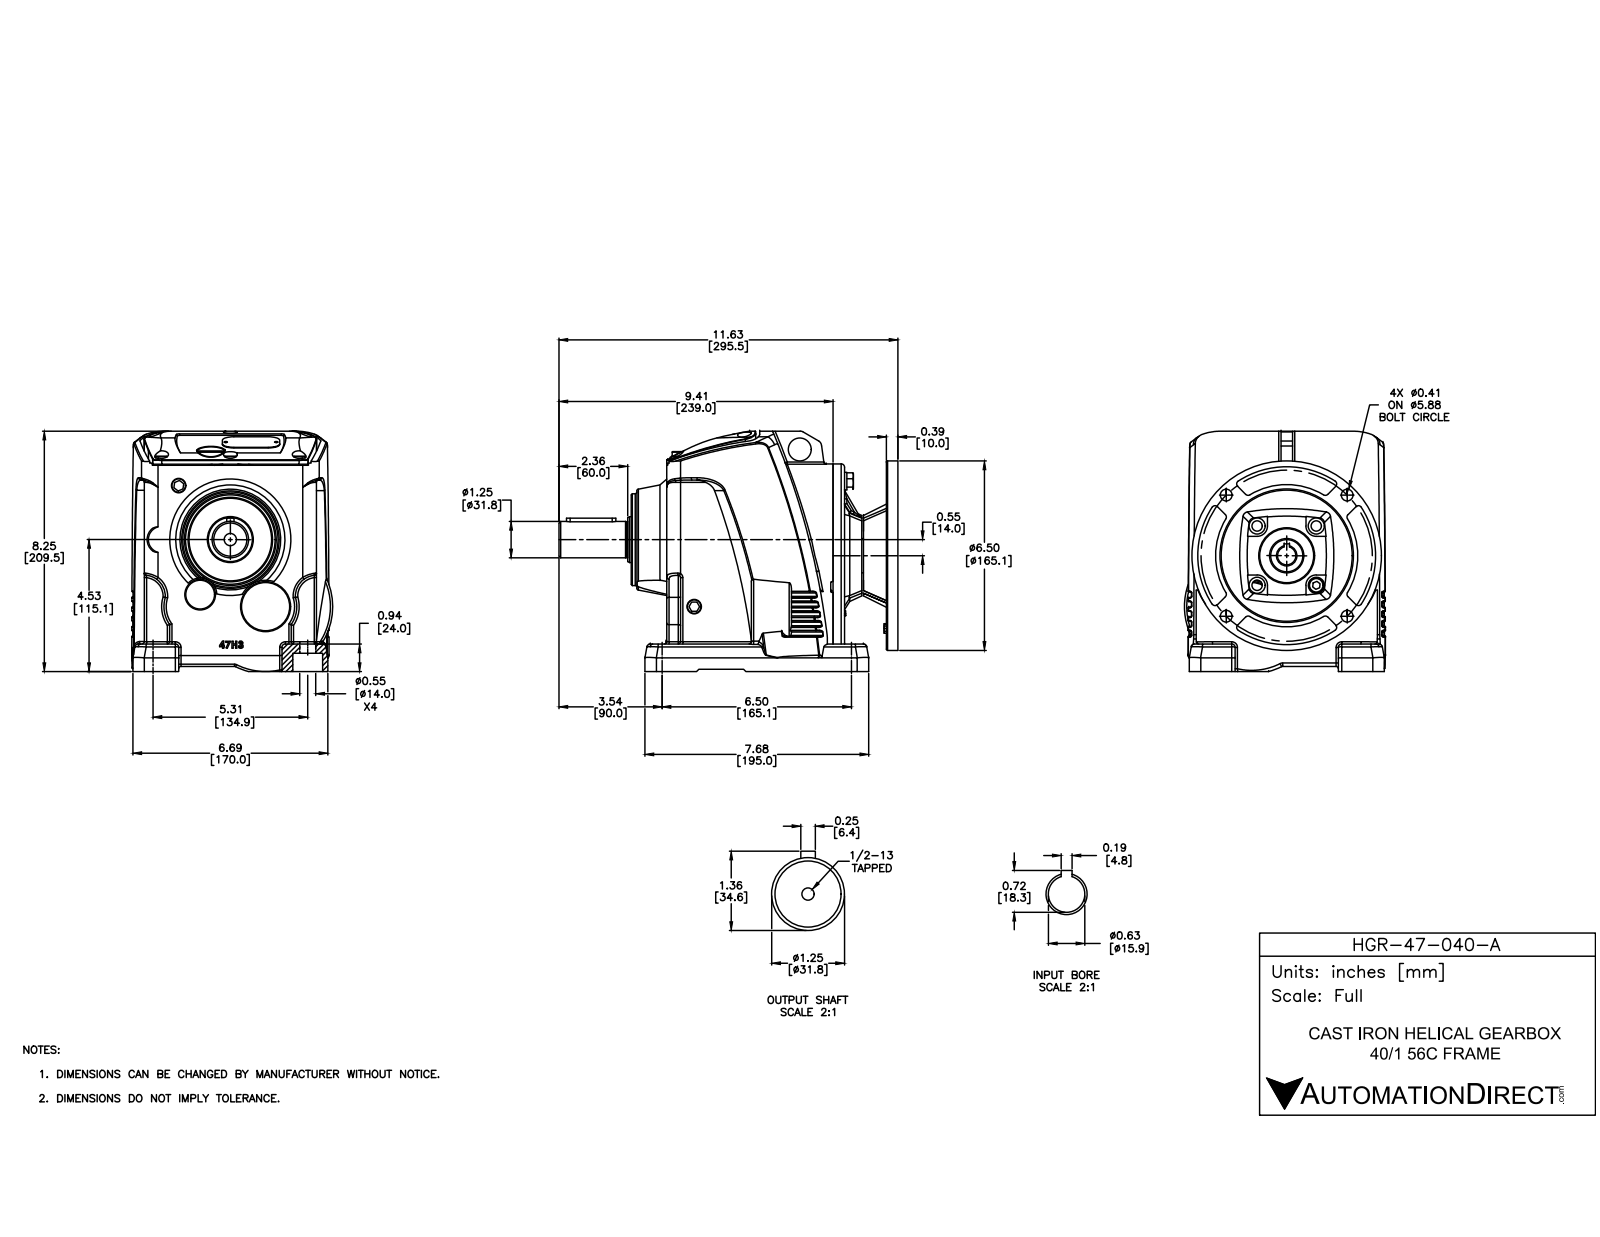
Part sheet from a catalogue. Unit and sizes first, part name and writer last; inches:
Units: inches
Overall size (bounding box): 11.631 × 8.248 × 6.9
Round holes (diameter × count): ⌀0.551 ×8, ⌀0.472 ×6, ⌀0.354 ×4, ⌀0.406 ×4, ⌀0.079 ×2, ⌀0.332 ×1, ⌀0.422 ×1, ⌀0.625 ×1, ⌀0.787 ×1, ⌀0.945 ×1, ⌀1.181 ×1, ⌀1.575 ×1
Round bosses / shafts (diameter × count): ⌀0.512 ×9, ⌀0.606 ×4, ⌀0.394 ×3, ⌀6.5 ×1, ⌀6.299 ×1, ⌀3.15 ×1, ⌀2.835 ×1, ⌀1.85 ×1
Partial cylindrical surfaces — rounded edges, fillets, slot ends (radius × count): R0.118 ×45, R0.079 ×41, R0.039 ×20, R0.394 ×8, R0.354 ×6, R0.004 ×2, R0.02 ×2, R0.125 ×2
Main face-to-face distances: 5.709, 0.391, 5.118, 1.828, 7.537, 0.394, 0.039, 1.299, 1.437, 6.1
Hole centre spacings: 1.848, 2.132, 3.27, 3.717, 5.08, 2.559, 1.437, 1.5
Volume: 273.5 in³ · Surface area: 658.5 in²
Bodies: 25 solids, 1163 faces (349 planar, 324 cylindrical, 490 other)
Part name (STEP PRODUCT): HGR-47-040-A
STEP written by: SolidWorks 2015 (CONFIG_CONTROL_DESIGN)
